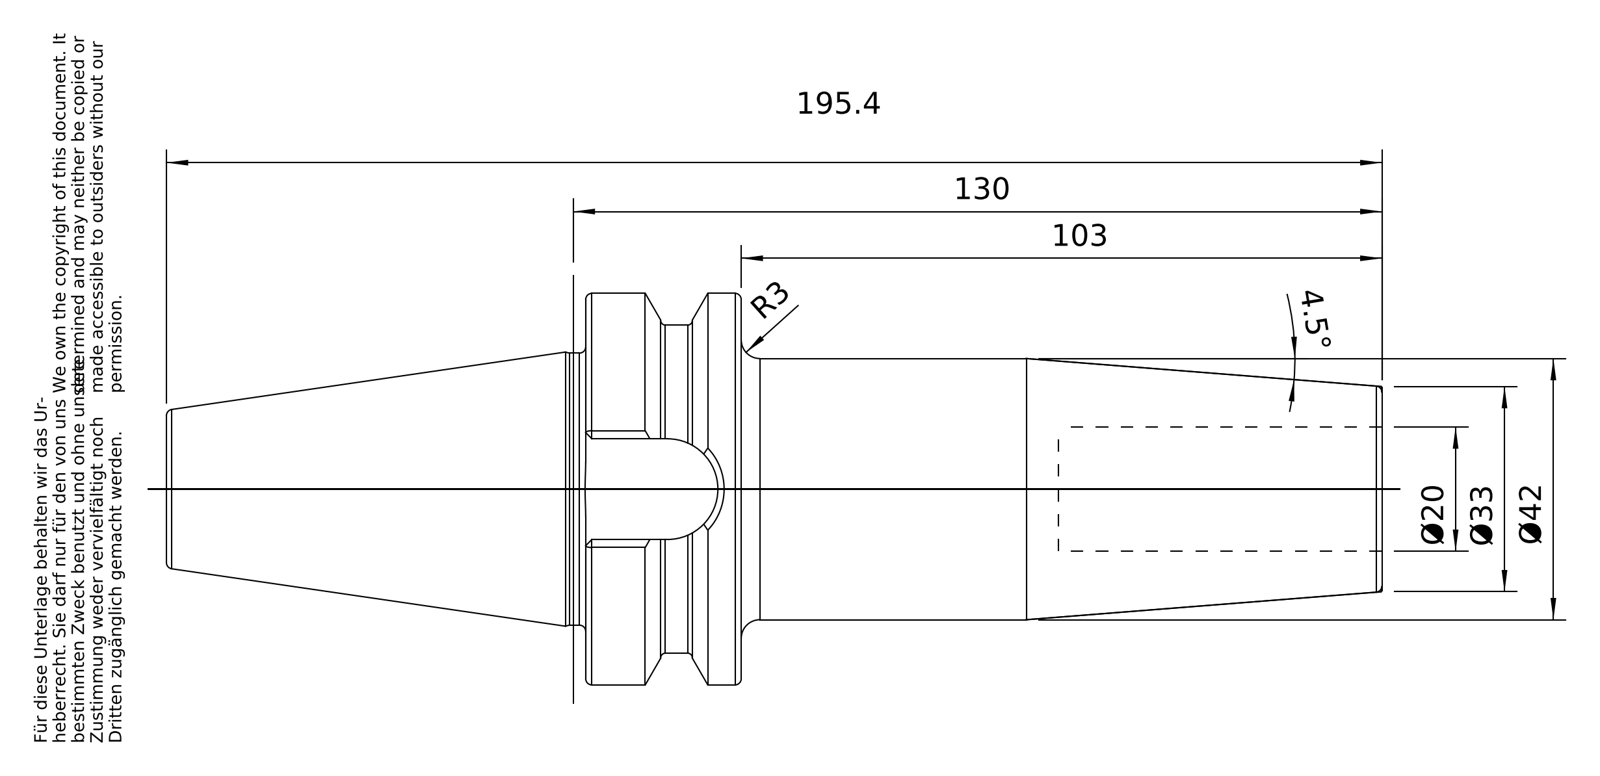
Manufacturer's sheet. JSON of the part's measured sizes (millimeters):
{"part_name": "40-644-20", "step_written_by": "PRO/ENGINEER BY PARAMETRIC TECHNOLOGY CORPORATION, 2010430 (CONFIG_CONTROL_DESIGN)", "units": "millimeters", "bodies": {"solids": 1, "faces": 96, "planar": 26, "cylindrical": 22, "other": 48}, "overall_size": [195.4, 62.98, 62.98], "volume_mm3": 236988, "surface_area_mm2": 37170, "round_holes": [[13.84, 1], [17.01, 1], [17.5, 1], [20, 1]], "round_bosses_or_shafts": [[62.98, 1], [52.75, 1], [43.75, 1], [42, 1], [16.01, 1]], "partial_cylinders_radius": [[8.1, 1]], "face_to_face_distances": [25, 128, 103, 44.9, 76, 51, 52, 16.2, 67.4, 92.4]}
